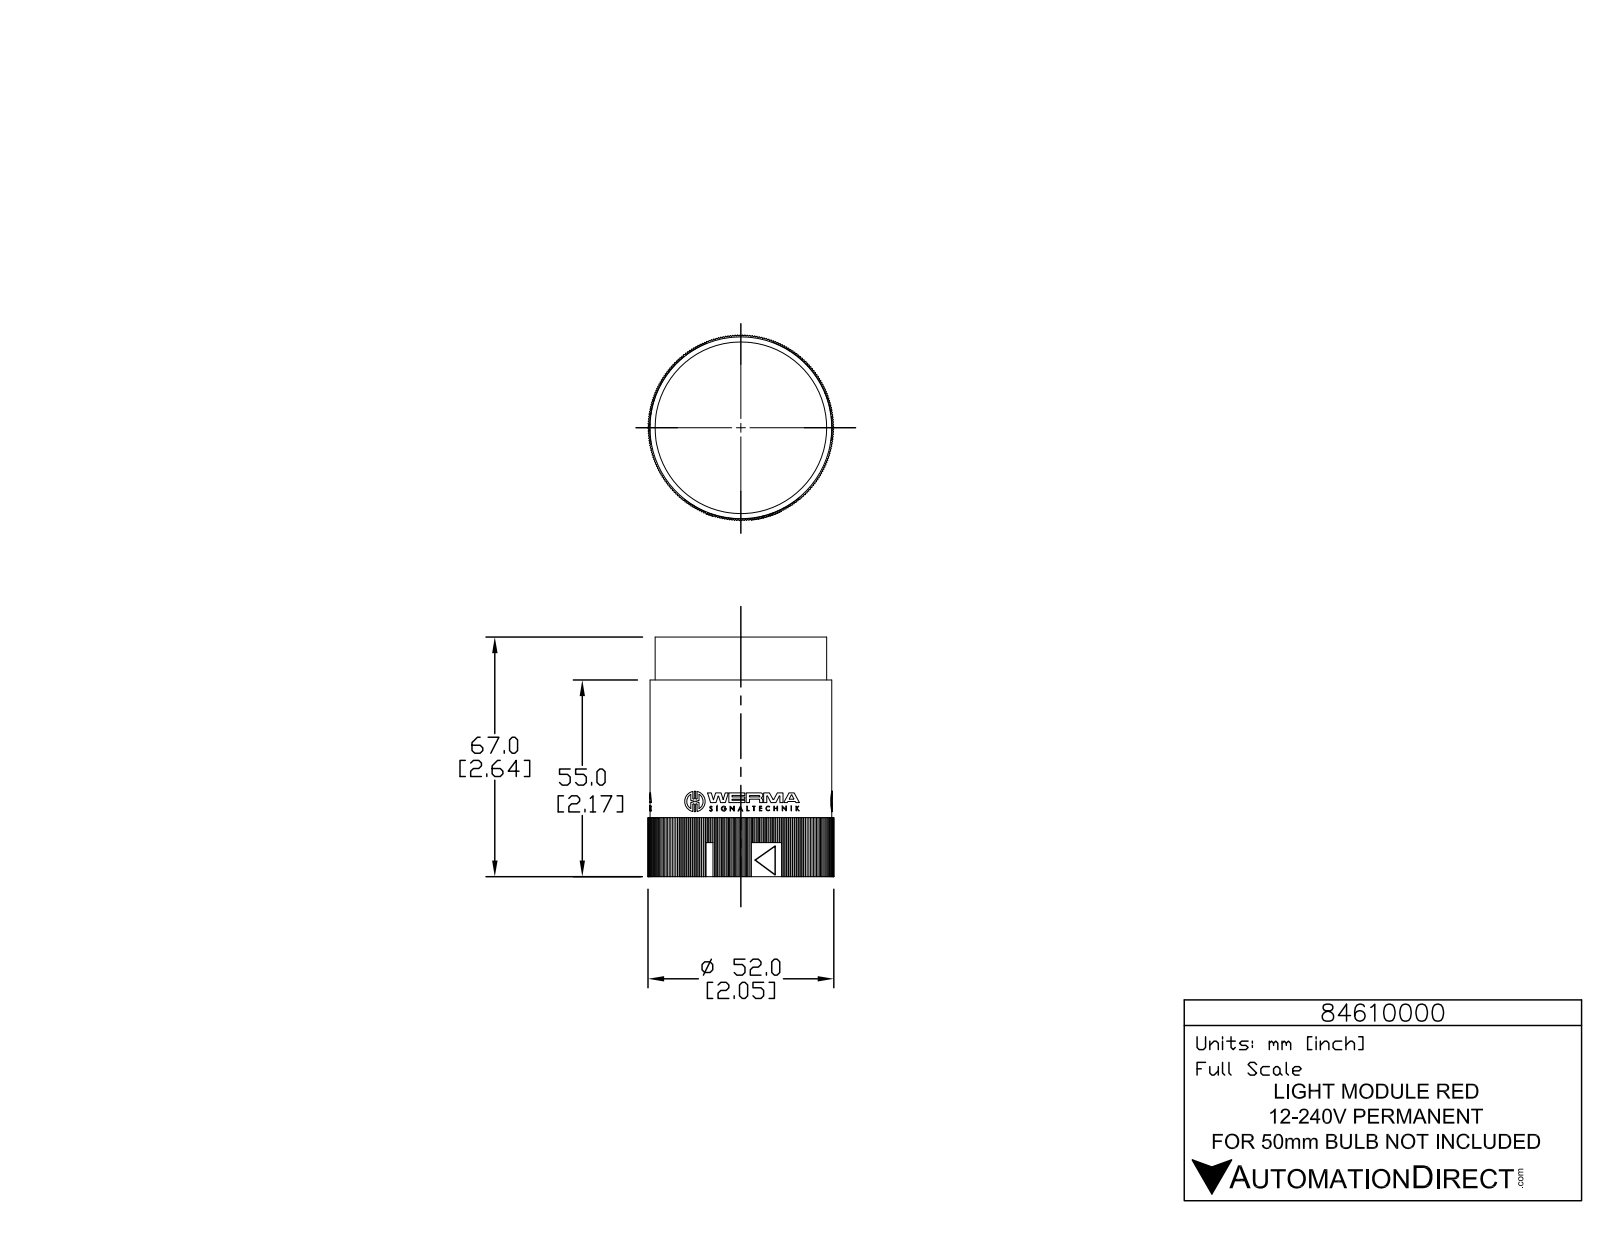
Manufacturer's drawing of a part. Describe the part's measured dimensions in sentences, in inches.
The part is named "84610000". Its 3-D file was written by "SolidWorks 2015 (AUTOMOTIVE_DESIGN)". It is 1 solid with 1265 faces: 1020 planar, 245 cylindrical and 0 other. Overall it measures 2.638 by 2.047 by 2.047 inches. Its volume is 6.873 cubic inches and its surface area 27.62 square inches. Round holes: 3 of diameter 0.039, 1 of diameter 1.898. Round bosses or shafts: 3 of diameter 0.226, 3 of diameter 0.056, 1 of diameter 2.002, 1 of diameter 1.89. Partial cylindrical surfaces (rounded edges, fillets, slot ends): 6 of radius 0.008, 6 of radius 0.008, 6 of radius 0.008, 6 of radius 0.131, 3 of radius 0.004, 3 of radius 0.005, 3 of radius 0.008, 3 of radius 0.008. The main face-to-face distances are 2.165, 1.428, 1.429, 1.429, 0.472, 2.638, 1.428, 1.428, 1.693, 1.988.
